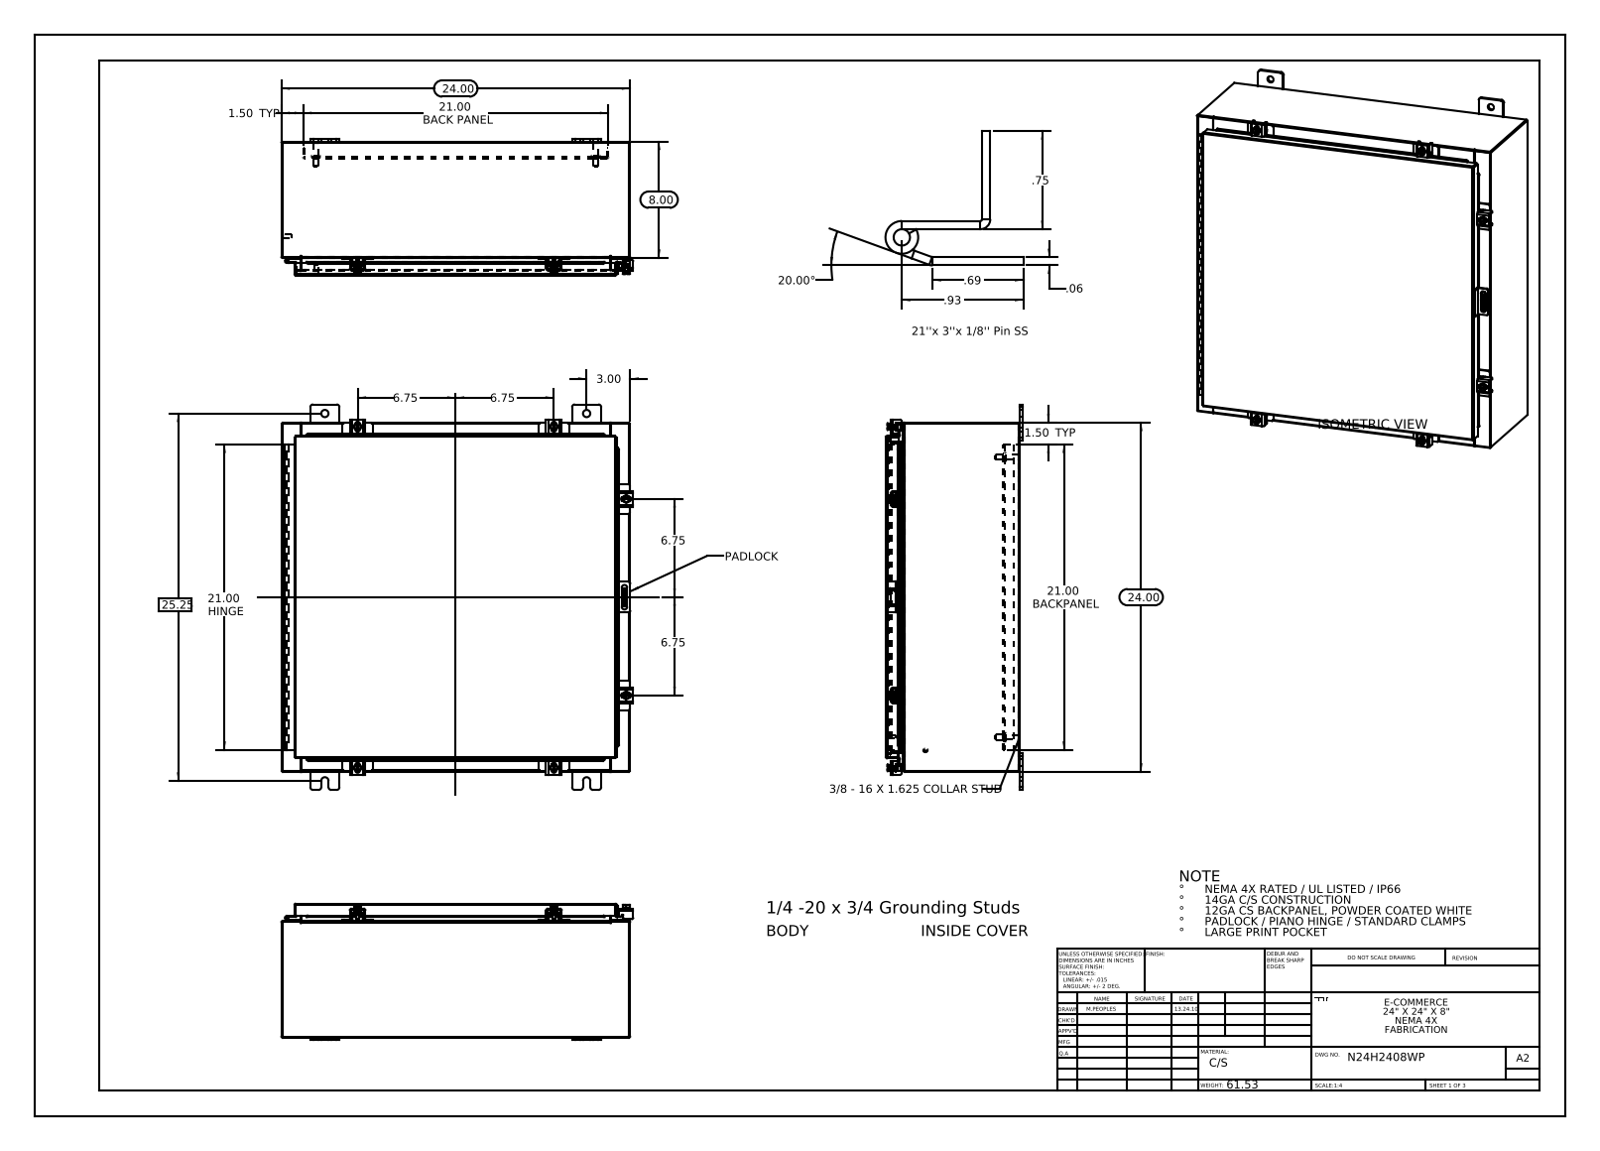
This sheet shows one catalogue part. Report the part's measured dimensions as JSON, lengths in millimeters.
{"part_name": "N24H2408SSWP Hinge Enclosure Side2; N24H2408SSWP 22104005_DEFAULT; N24H2408SSWP Standard Clamps; N24H2408SSWP Mounting Feet (+8 more)", "step_written_by": "SolidWorks 2013 (CONFIG_CONTROL_DESIGN)", "units": "millimeters", "bodies": {"solids": 49, "faces": 1735, "planar": 914, "cylindrical": 713, "other": 108}, "overall_size": [673.1, 615, 238.5], "volume_mm3": 3543000, "surface_area_mm2": 3505000, "round_holes": [[12.7, 8], [5.4, 6], [6.6, 6], [3.2, 2]], "round_bosses_or_shafts": [[6.4, 7], [12.7, 6], [10.1, 6], [15.9, 4], [9.5, 4], [8.4, 4], [8, 2], [6, 2]], "partial_cylinders_radius": [[1.5, 30], [0.3, 25], [4.8, 24], [2.2, 21], [3, 12], [3.6, 12], [3.2, 10], [1.3, 9]], "face_to_face_distances": [1.9, 231.8, 607.7, 229.9, 233.7, 2.6, 25.4, 27.3, 204.5, 206.4], "hole_center_spacings": [419.3, 486, 547.2, 683.4, 342.9, 47.2, 57.8, 61.5]}
